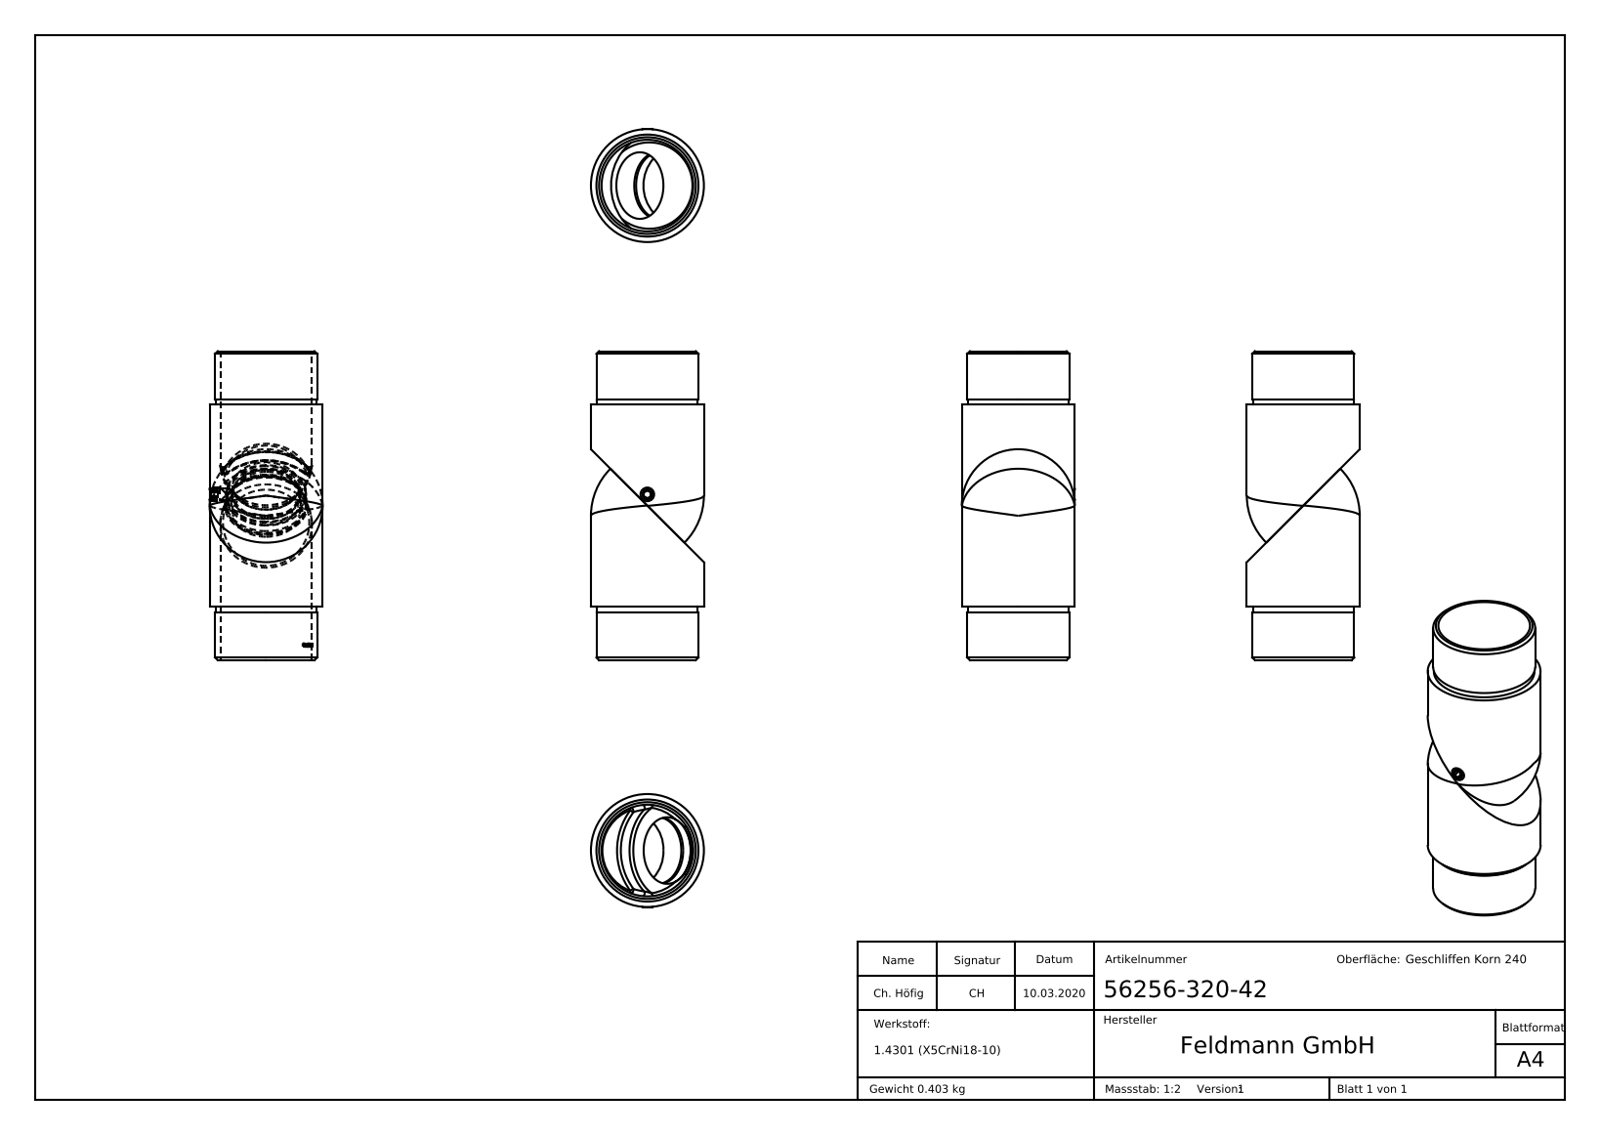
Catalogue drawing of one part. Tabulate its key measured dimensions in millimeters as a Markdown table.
| quantity | value |
| --- | --- |
| part name | DIN914; 56256-320-42; DIN914_DIN 914 M5x6; 56256-320-XX Teil1und2 (+2 more) |
| STEP written by | SolidWorks 2015 (CONFIG_CONTROL_DESIGN) |
| units | millimeters |
| bodies | 3 solids, 332 faces (137 planar, 45 cylindrical, 150 other) |
| overall size | 116 × 70 × 42.4 |
| volume | 51 028 mm³ |
| surface area | 32 284 mm² |
| round holes (diameter × count) | 25 × 2, 4.2 × 1, 34.4 × 1 |
| round bosses / shafts (diameter × count) | 42.4 × 1, 38.3 × 1, 37.8 × 1, 30 × 1, 5 × 1 |
| partial cylindrical surfaces (radius × count) | 16.2 × 1, 17.3 × 1, 19 × 1 |
| main face-to-face distances | 4, 76, 2, 14.49, 10.49, 6.5, 10.5, 3.99, 20, 96 |
